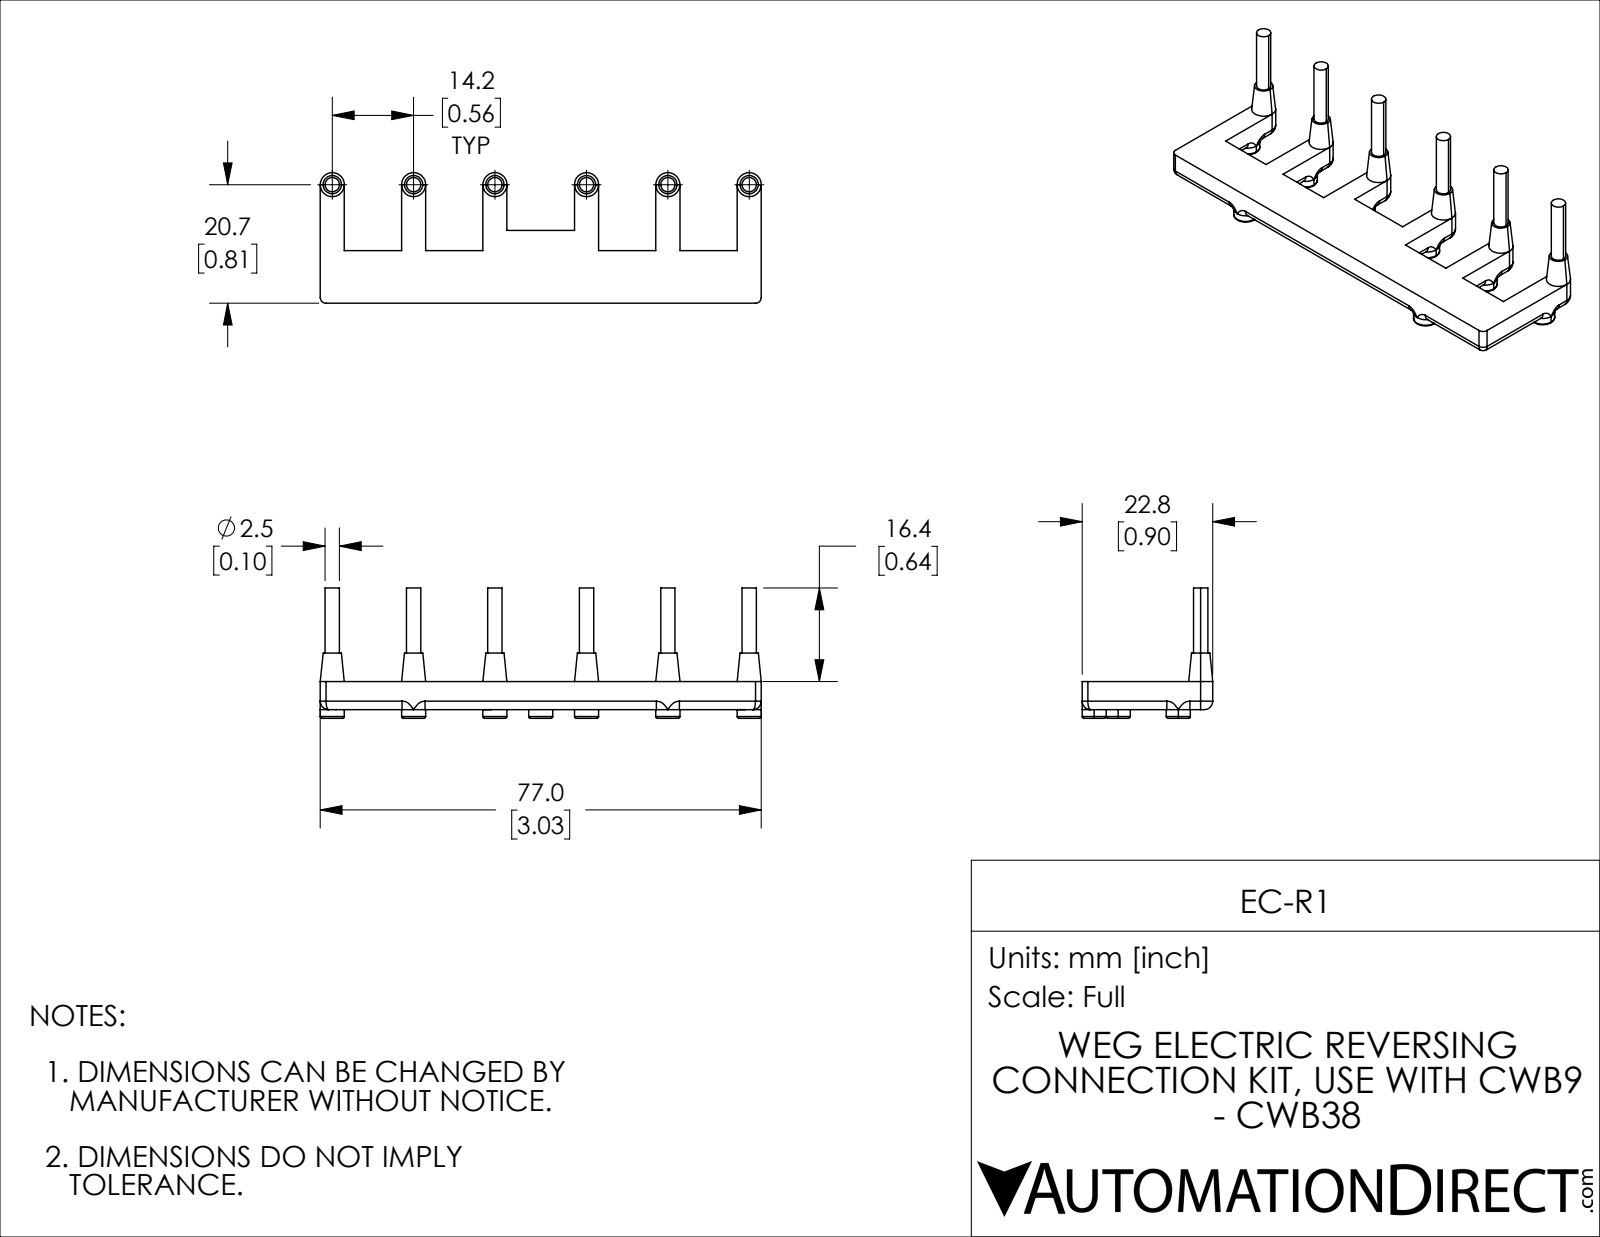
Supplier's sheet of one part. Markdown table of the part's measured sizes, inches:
| quantity | value |
| --- | --- |
| part name | EC-R1 |
| STEP written by | SolidWorks 2019 (CONFIG_CONTROL_DESIGN) |
| units | inches |
| bodies | 1 solid, 222 faces (56 planar, 64 cylindrical, 102 other) |
| overall size | 3.031 × 0.898 × 0.896 |
| volume | 0.362 in³ |
| surface area | 7.218 in² |
| partial cylindrical surfaces (radius × count) | 0.059 × 15, 0.083 × 15, 0.051 × 9, 0.049 × 6, 0.039 × 2 |
| main face-to-face distances | 0.193, 0.559, 0.165, 1.748, 2.307, 0.394, 0.724, 1.118, 1.189, 0.362 |
